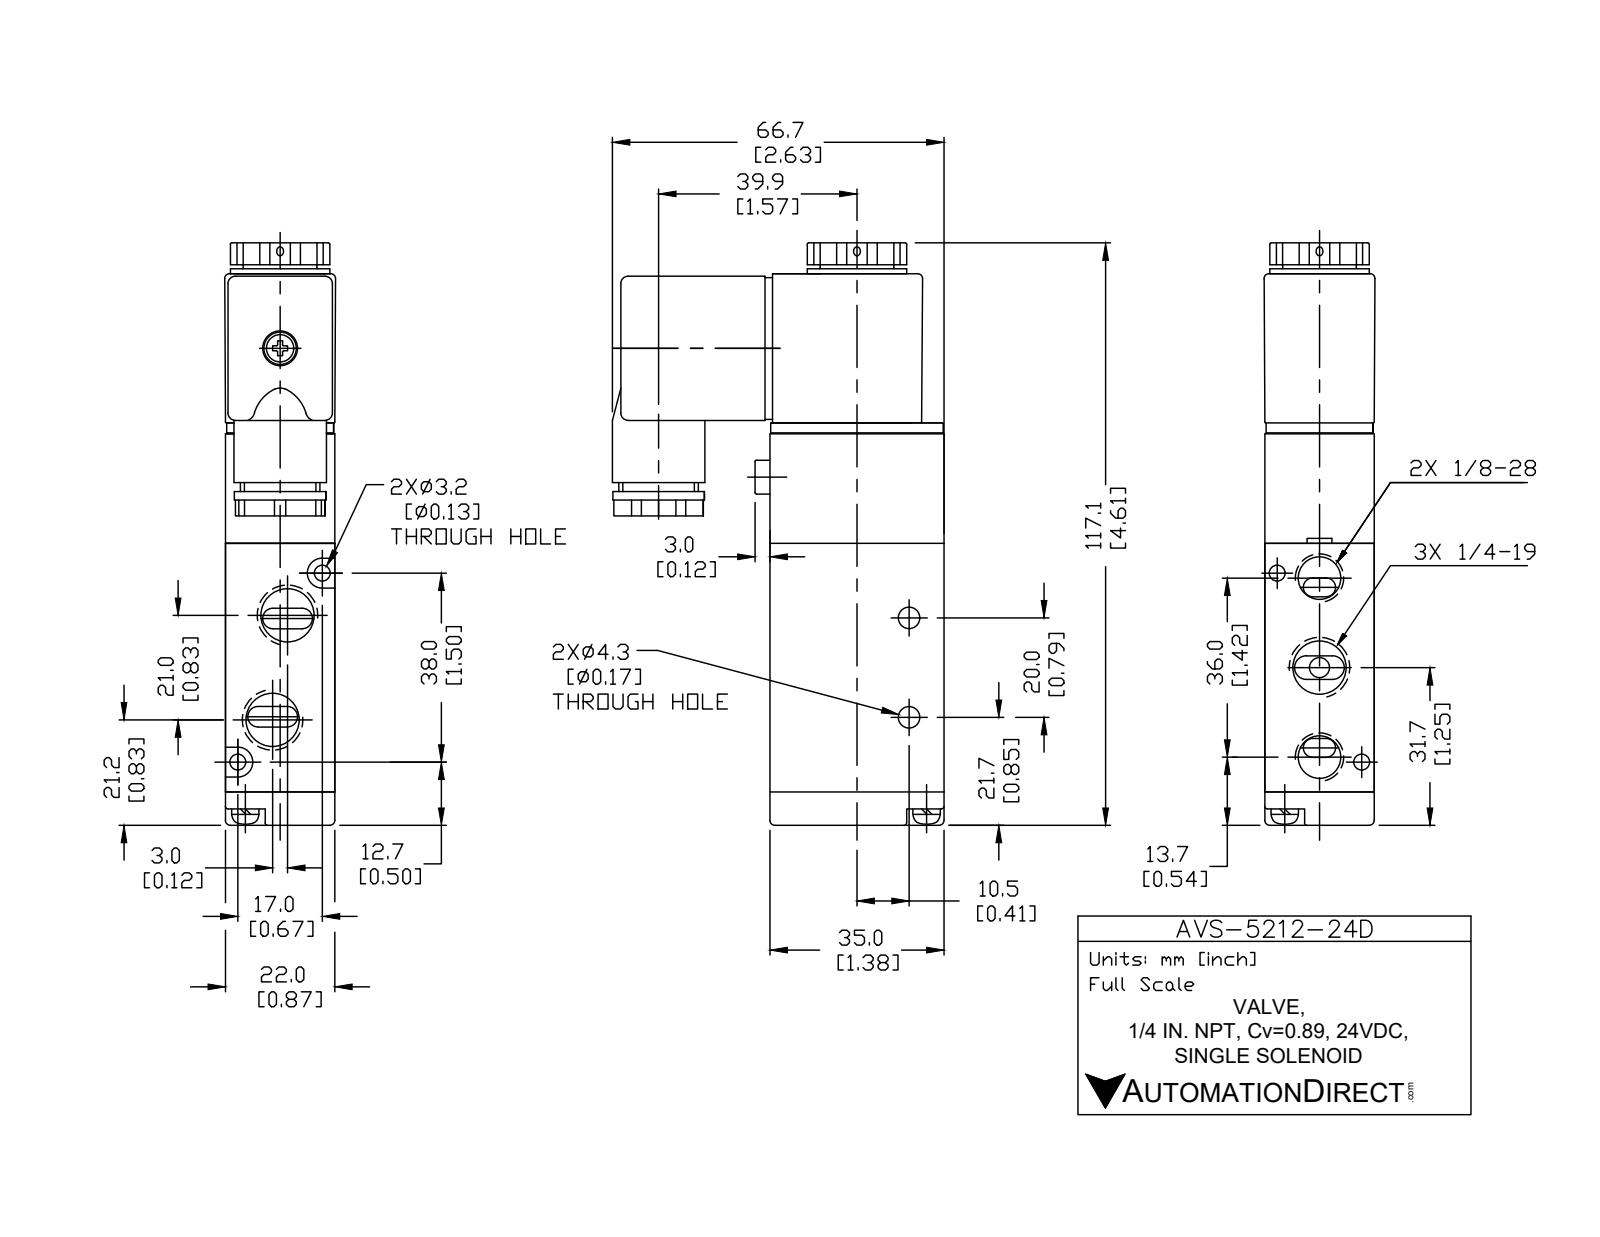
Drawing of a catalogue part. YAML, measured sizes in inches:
part_name: "AVS-5212-24D"
step_written_by: "SolidWorks 2015 (CONFIG_CONTROL_DESIGN)"
units: inches
bodies: {solids: 4, faces: 195, planar: 91, cylindrical: 77, other: 27}
overall_size: [4.61, 2.626, 0.866]
volume: 6.023
surface_area: 39.3
round_holes:
  - {diameter: 0.438, count: 3}
  - {diameter: 0.169, count: 2}
  - {diameter: 0.332, count: 2}
  - {diameter: 0.126, count: 1}
  - {diameter: 0.13, count: 1}
  - {diameter: 0.366, count: 1}
round_bosses_or_shafts:
  - {diameter: 0.787, count: 1}
  - {diameter: 0.732, count: 1}
  - {diameter: 0.724, count: 1}
  - {diameter: 0.63, count: 1}
  - {diameter: 0.583, count: 1}
  - {diameter: 0.264, count: 1}
partial_cylinders:
  - {radius: 0.059, count: 12}
  - {radius: 0.061, count: 10}
  - {radius: 0.02, count: 8}
  - {radius: 0.039, count: 5}
  - {radius: 0.118, count: 2}
face_to_face_distances: [0.866, 0.02, 1.969, 0.846, 1.378, 0.264, 0.827, 4.346, 2.232, 1.181]
hole_center_spacings: [0.337, 0.709, 0.819, 1.494, 0.297, 0.308, 0.415, 0.415]
